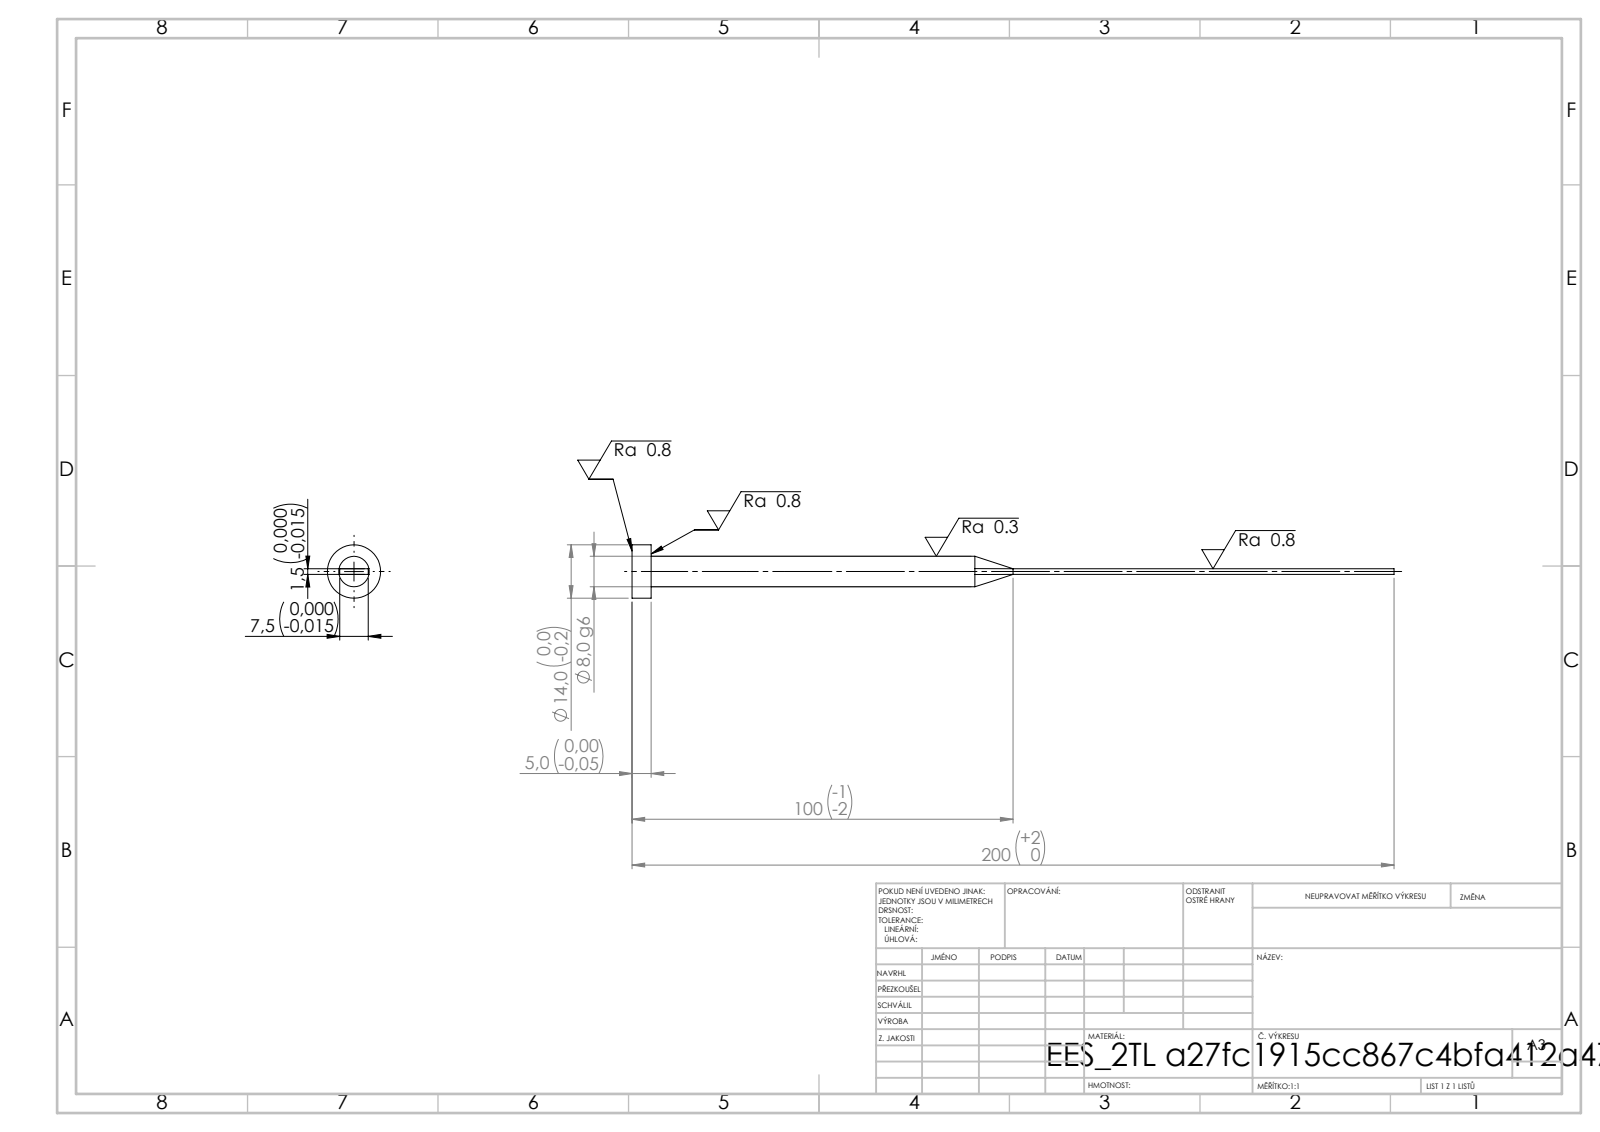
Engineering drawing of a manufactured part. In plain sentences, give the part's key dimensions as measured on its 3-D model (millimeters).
Its 3-D file was written by "SolidWorks 2019 (CONFIG_CONTROL_DESIGN)". It is 1 solid with 15 faces: 7 planar, 4 cylindrical and 4 other. Overall it measures 200 by 14 by 14 millimeters. Its volume is 6 460 cubic millimeters and its surface area 4 636 square millimeters. Round bosses or shafts: 1 of diameter 14, 1 of diameter 8. The main face-to-face distances are 1.5, 7.5, 5, 200, 195.
